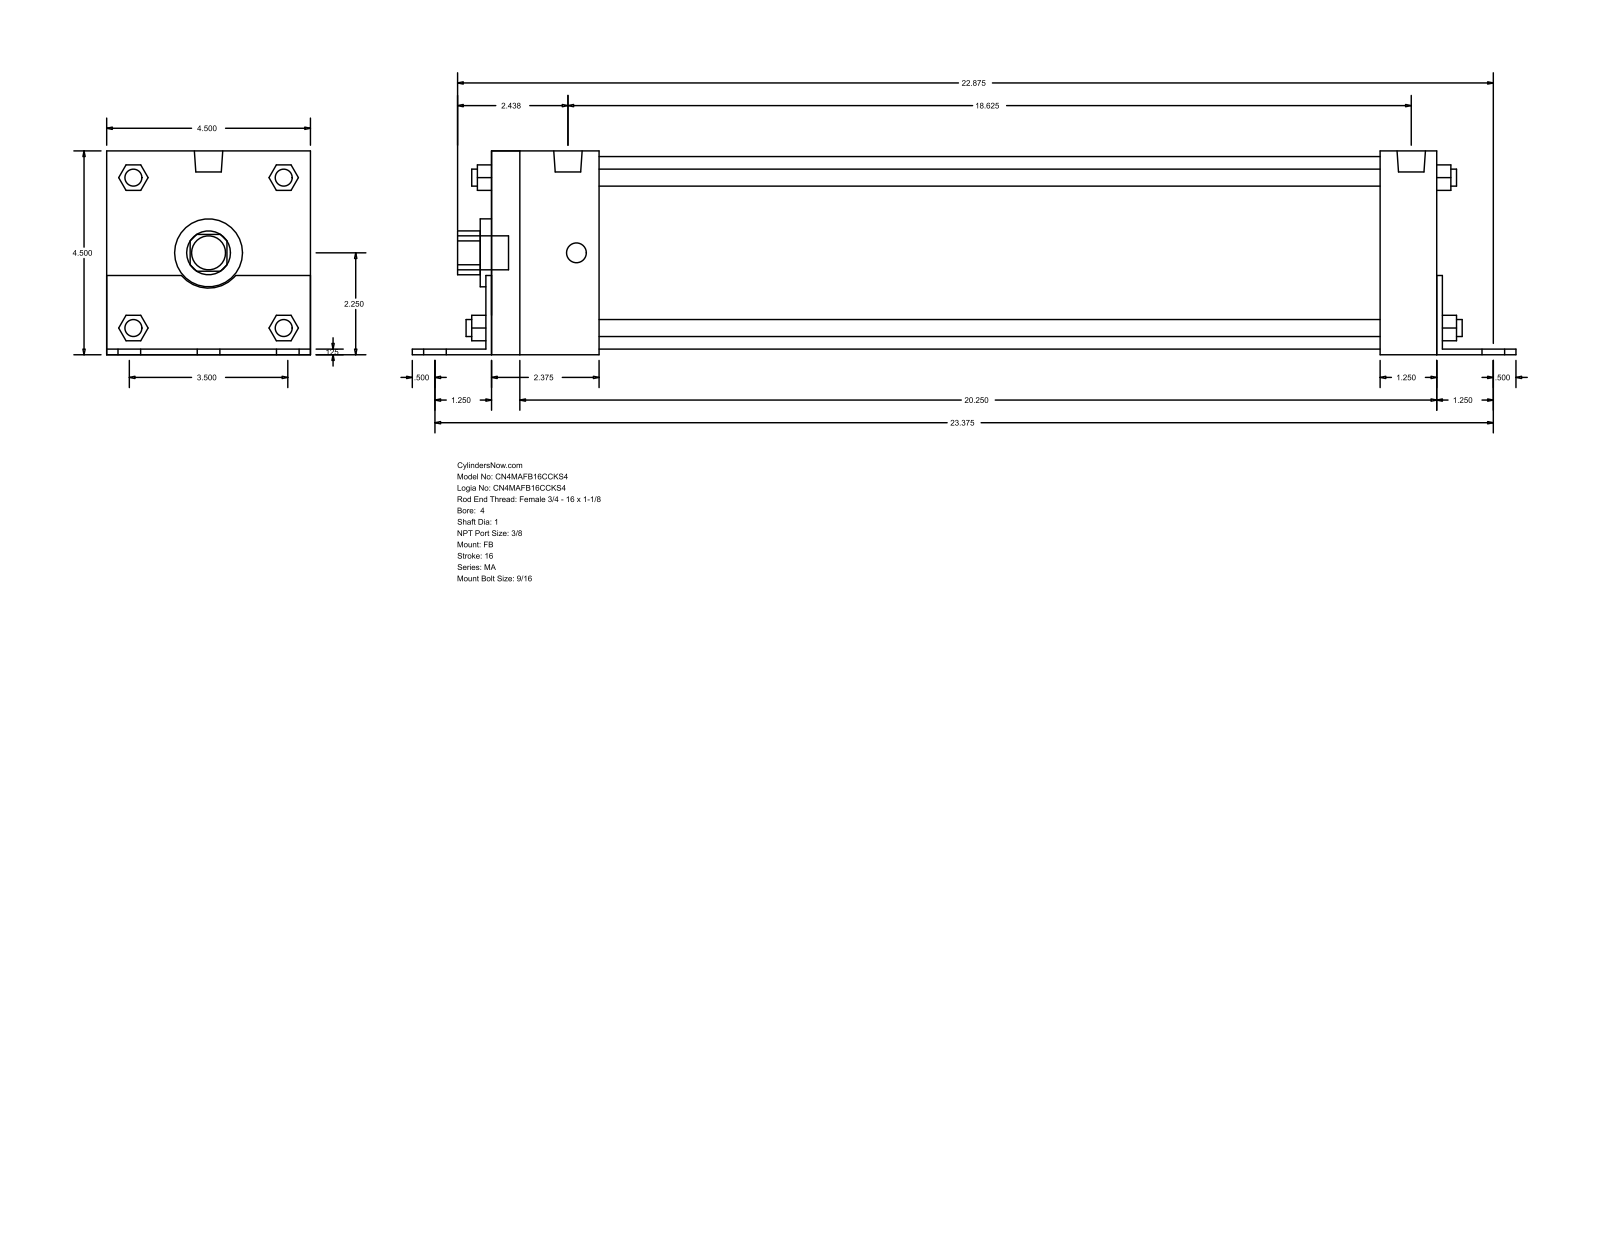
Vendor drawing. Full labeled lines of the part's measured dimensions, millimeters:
Part name (STEP PRODUCT): MA_FB__0400_1
STEP written by: GSSL Pune (CONFIG_CONTROL_DESIGN)
Units: millimetres
Bodies: 0 solids, 140 faces (105 planar, 35 cylindrical, 0 other)
Overall size (bounding box): 619.12 × 114.35 × 114.3
Round holes (diameter × count): ⌀25.4 ×1, ⌀38.1 ×1, ⌀107.95 ×1
Round bosses / shafts (diameter × count): ⌀14.29 ×6, ⌀11.11 ×4, ⌀9.53 ×4, ⌀15.93 ×2, ⌀19.05 ×1
Partial cylindrical surfaces — rounded edges, fillets, slot ends (radius × count): R12.29 ×1, R19.81 ×1
Main face-to-face distances: 114.3, 3.17, 114.35, 3.12, 111.18, 530.22, 3.18, 536.57, 533.4, 533.39
